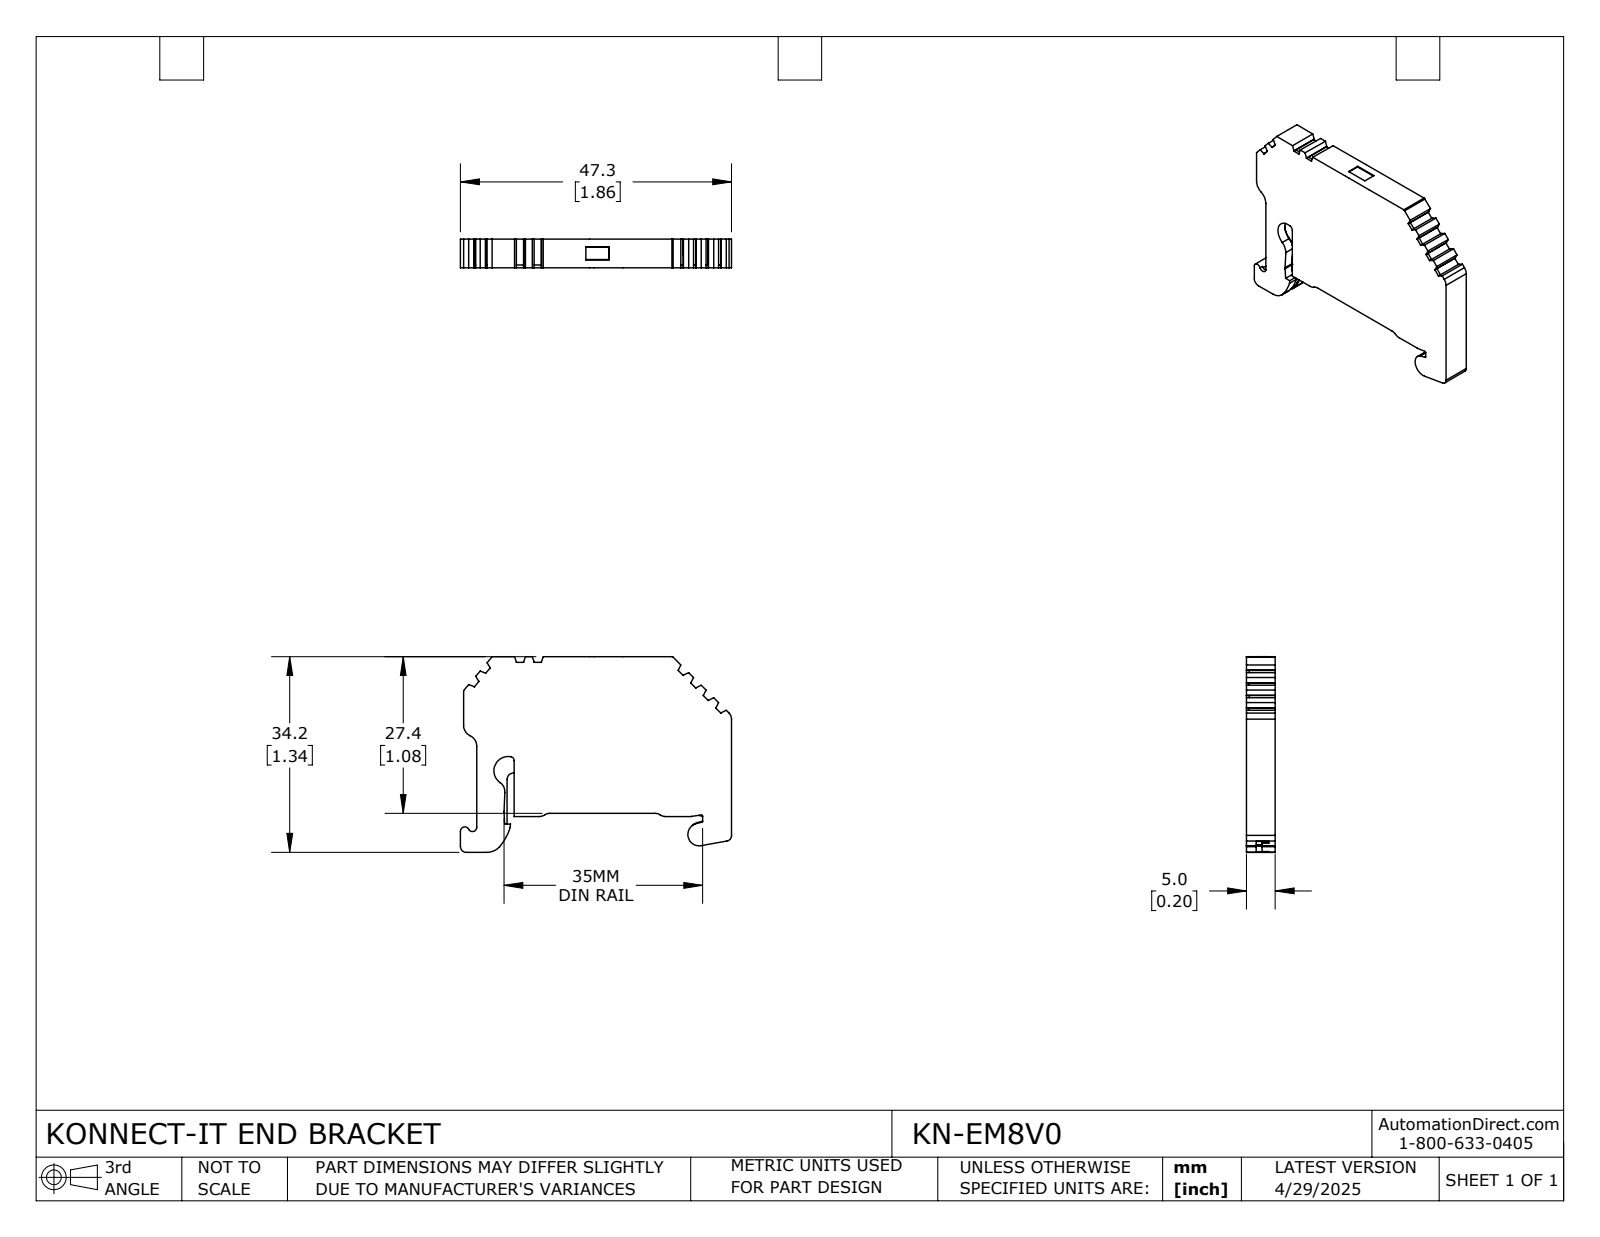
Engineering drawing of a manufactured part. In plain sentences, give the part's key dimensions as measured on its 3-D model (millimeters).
The part is named "KN-EM8V0". Its 3-D file was written by "SolidWorks 2024 (CONFIG_CONTROL_DESIGN)". It is 1 solid with 244 faces: 156 planar, 87 cylindrical and 1 other. Overall it measures 47.34 by 34.16 by 5 millimeters. Its volume is 6 143 cubic millimeters and its surface area 3 548 square millimeters. Partial cylindrical surfaces (rounded edges, fillets, slot ends): 17 of radius 0.5, 5 of radius 1.5, 4 of radius 2, 3 of radius 0.2, 3 of radius 0.3, 3 of radius 1, 2 of radius 0.4, 2 of radius 0.75. The main face-to-face distances are 5, 27.35, 44.5, 0.55, 2.93, 6.55, 37.95, 27.9, 2.29, 8.84.
